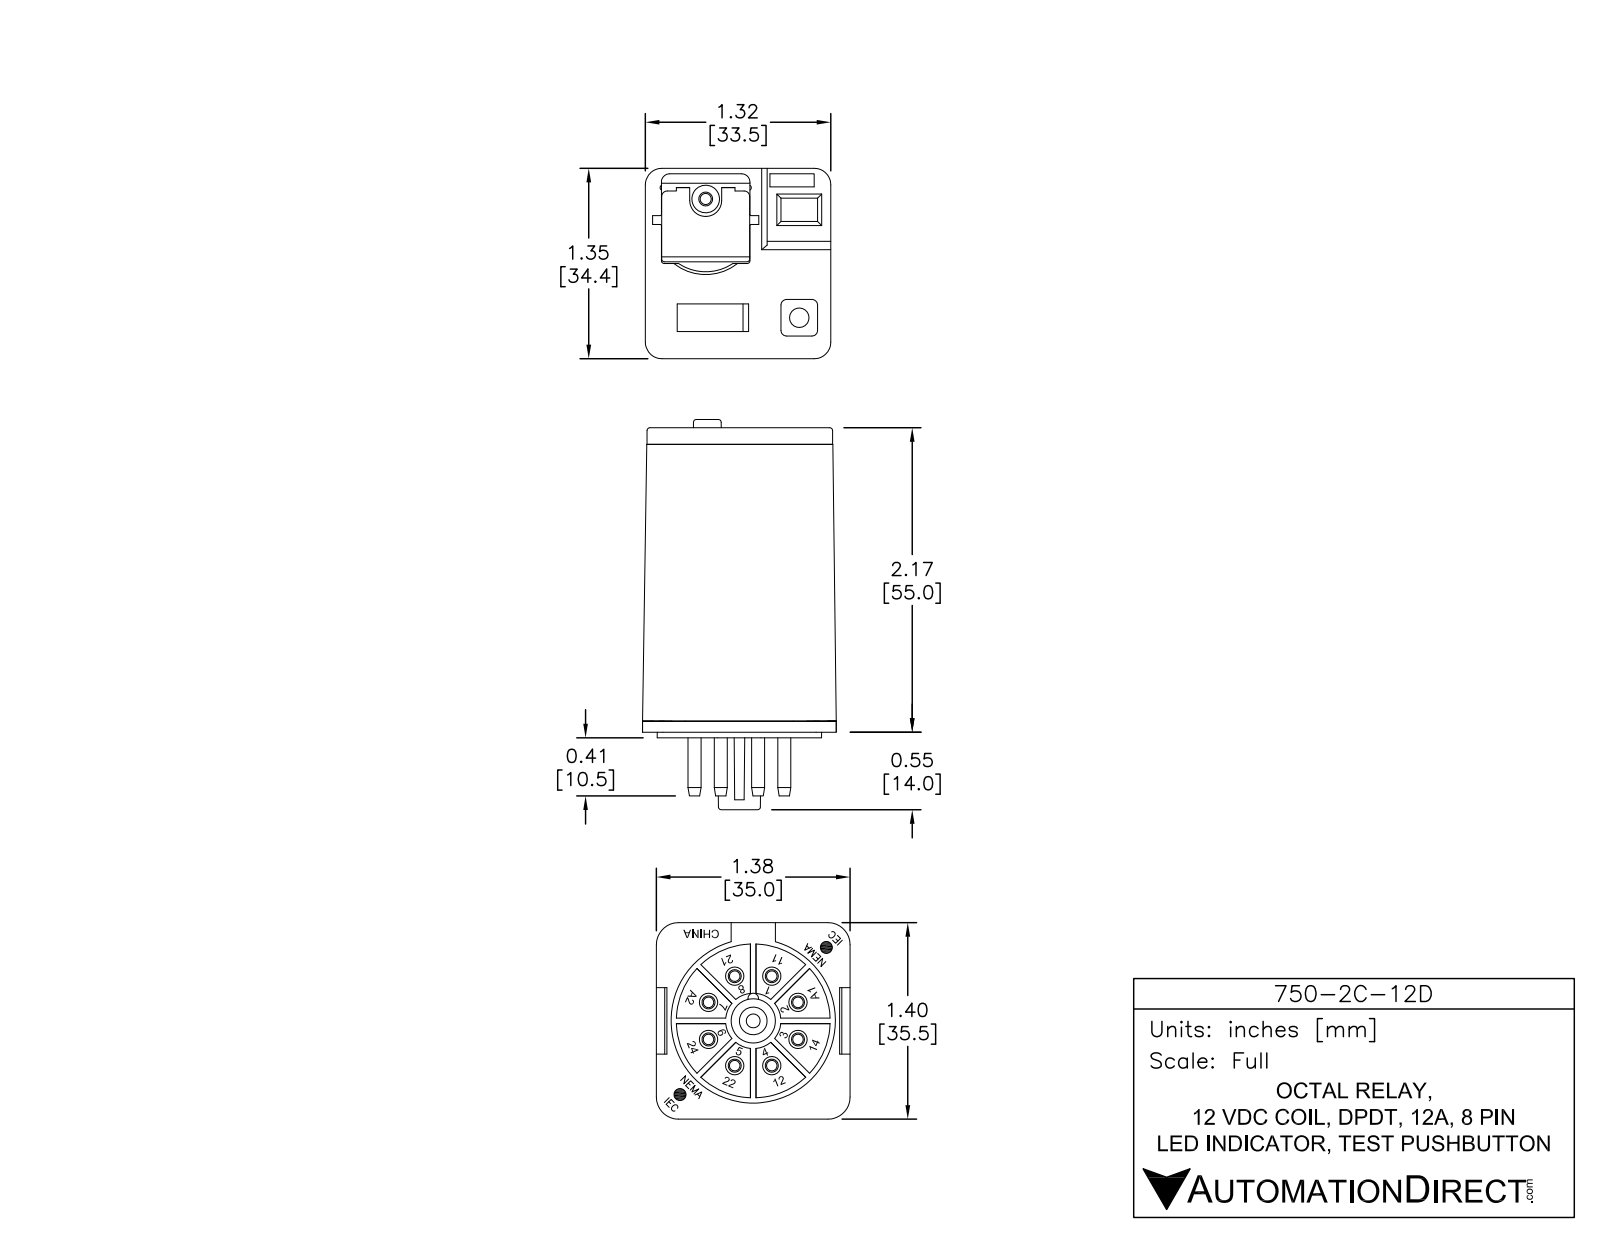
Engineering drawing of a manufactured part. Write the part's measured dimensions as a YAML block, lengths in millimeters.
part_name: "750-2C-12D"
step_written_by: "SolidWorks 2013 (AUTOMOTIVE_DESIGN)"
units: millimeters
bodies: {solids: 5, faces: 349, planar: 180, cylindrical: 86, other: 83}
overall_size: [69.6, 35.12, 35]
volume: 67512
surface_area: 16450
round_holes:
  - {diameter: 2.5, count: 1}
  - {diameter: 27.5, count: 1}
round_bosses_or_shafts:
  - {diameter: 3, count: 8}
  - {diameter: 2.3, count: 8}
  - {diameter: 29.5, count: 1}
  - {diameter: 8, count: 1}
  - {diameter: 4.8, count: 1}
  - {diameter: 0.83, count: 1}
partial_cylinders:
  - {radius: 0.5, count: 4}
  - {radius: 3, count: 4}
  - {radius: 0.25, count: 2}
  - {radius: 1, count: 2}
  - {radius: 0.75, count: 1}
  - {radius: 0.99, count: 1}
  - {radius: 2.5, count: 1}
  - {radius: 5, count: 1}
face_to_face_distances: [35, 50, 54.75, 3, 1.75, 51.75, 53, 1, 53.35, 1.4]
hole_center_spacings: [12.69]
